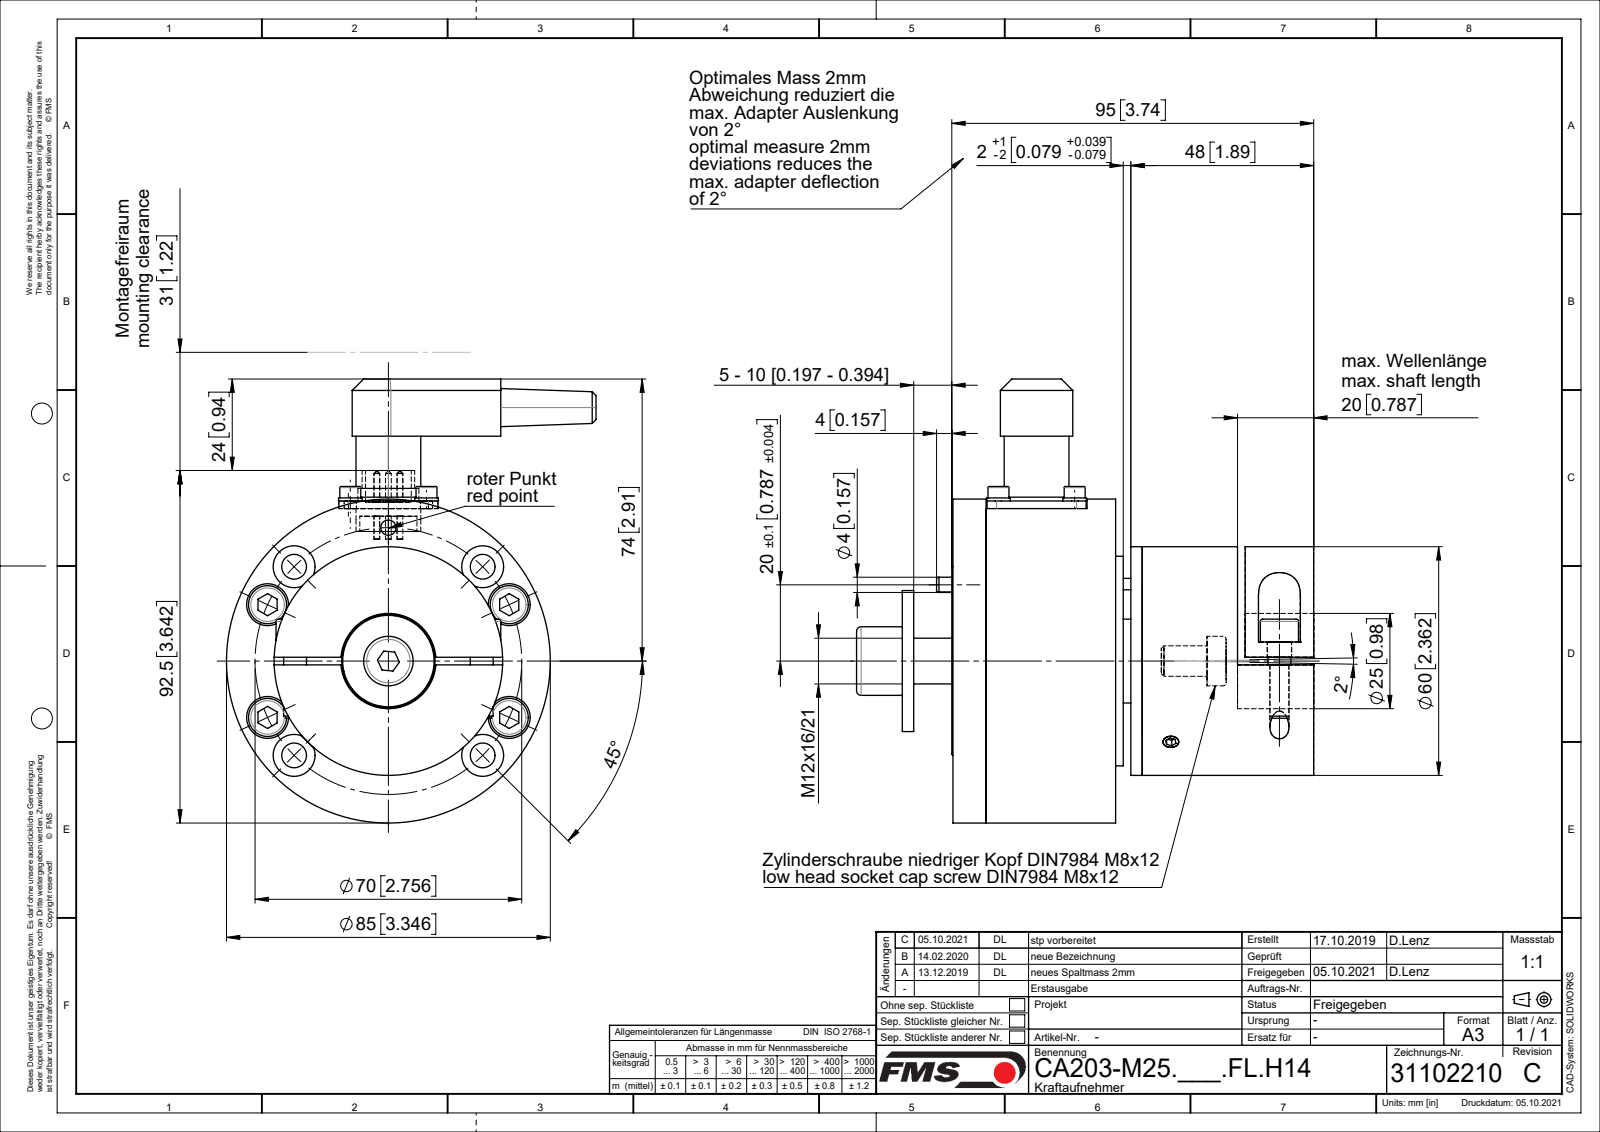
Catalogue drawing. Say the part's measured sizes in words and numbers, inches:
The part is named "070403-1_01; 070908-1_stp_01; Federringe_DIN127A_M03; Gew-Sti-I6kt-Zapfen DIN915_M5x10 (+8 more)". Its 3-D file was written by "SolidWorks 2018 (CONFIG_CONTROL_DESIGN)". It is 43 solids with 803 faces: 278 planar, 333 cylindrical and 192 other. Overall it measures 4.724 by 4.587 by 3.819 inches. Its volume is 19.24 cubic inches and its surface area 176.4 square inches. Round holes: 8 of diameter 0.098, 8 of diameter 0.256, 8 of diameter 0.433, 6 of diameter 0.197, 5 of diameter 0.079, 5 of diameter 0.157, 4 of diameter 0.122, 4 of diameter 0.126, 4 of diameter 0.142, 4 of diameter 0.276, 2 of diameter 0.118, 2 of diameter 0.252. Round bosses or shafts: 8 of diameter 0.118, 7 of diameter 0.236, 6 of diameter 0.394, 5 of diameter 0.059, 4 of diameter 0.244, 4 of diameter 0.224, 4 of diameter 0.217, 1 of diameter 3.346. Partial cylindrical surfaces (rounded edges, fillets, slot ends): 4 of radius 0.098, 2 of radius 0.197, 2 of radius 0.217, 1 of radius 0.374. The main face-to-face distances are 0.079, 1.772, 1.614, 0.394, 1.181, 0.118, 2.362, 1.339, 1.969, 0.866. The hole center spacings are 1.378, 0.787, 0.976, 0.992, 1.291, 2.013, 2.223, 0.236.
